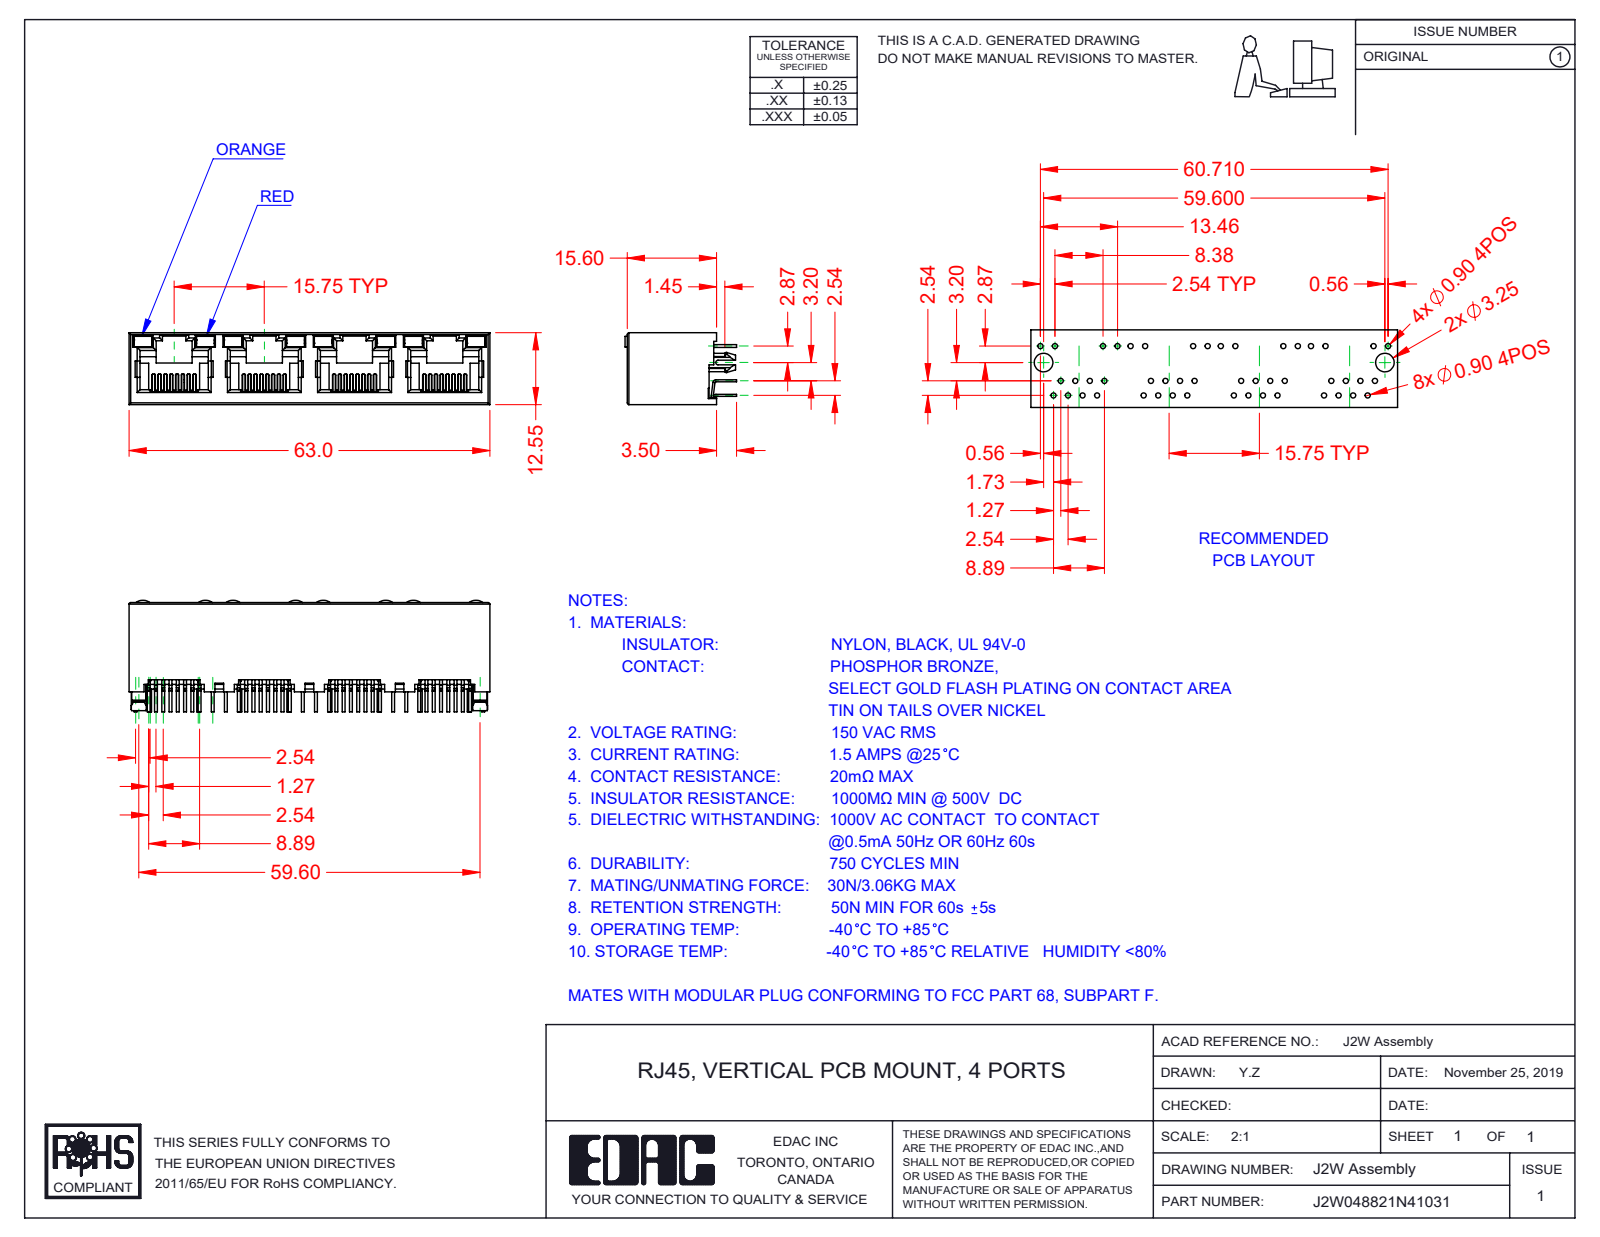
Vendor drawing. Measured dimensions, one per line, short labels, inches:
name: 2W LED RH_2-Red; 2W LED LH_4-Orange; J2W048821N42131; 2W Contact Lock (+2 more)
written by: SolidWorks 2016 (CONFIG_CONTROL_DESIGN)
unit: in
bodies: 45 solids, 3135 faces (2600 planar, 477 cylindrical, 58 other)
size: 2.48 × 0.768 × 0.494
volume: 0.326 in³; area: 20.37 in²
rounds: 64× R0.006, 29× R0.008, 28× R0.02, 14× R0.012, 8× R0.018, 8× R0.079, 2× R0.01, 2× R0.059
face distances: 0.494, 0.469, 0.026, 0.62, 0.014, 0.059, 0.031, 0.024, 0.445, 1.24
